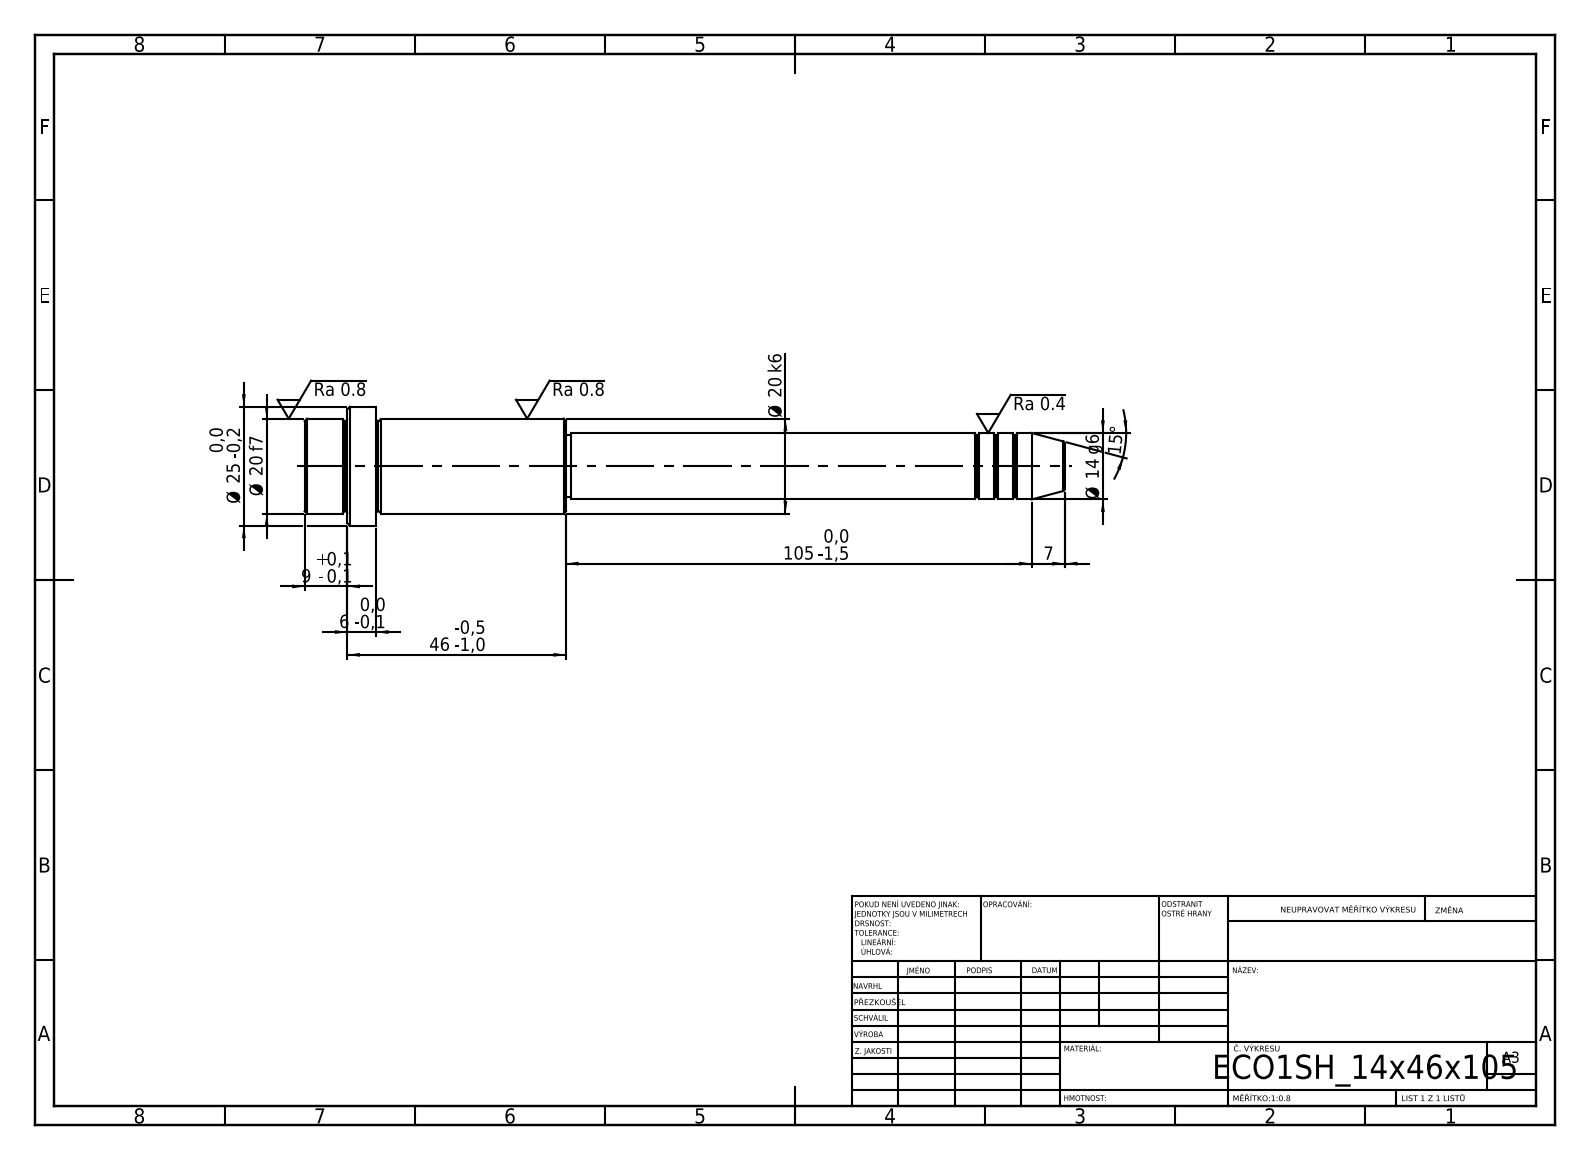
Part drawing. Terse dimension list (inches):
written by: SolidWorks 2019 (CONFIG_CONTROL_DESIGN)
unit: in
bodies: 1 solid, 52 faces (6 planar, 16 cylindrical, 30 other)
size: 6.299 × 0.984 × 0.984
volume: 2.081 in³; area: 14.19 in²
bosses: 1× ⌀0.984, 1× ⌀0.787, 1× ⌀0.551, 1× ⌀0.512
face distances: 0.591, 1.575, 2.165, 1.811, 0.236, 0.354, 4.134, 5.709, 5.945, 6.299
